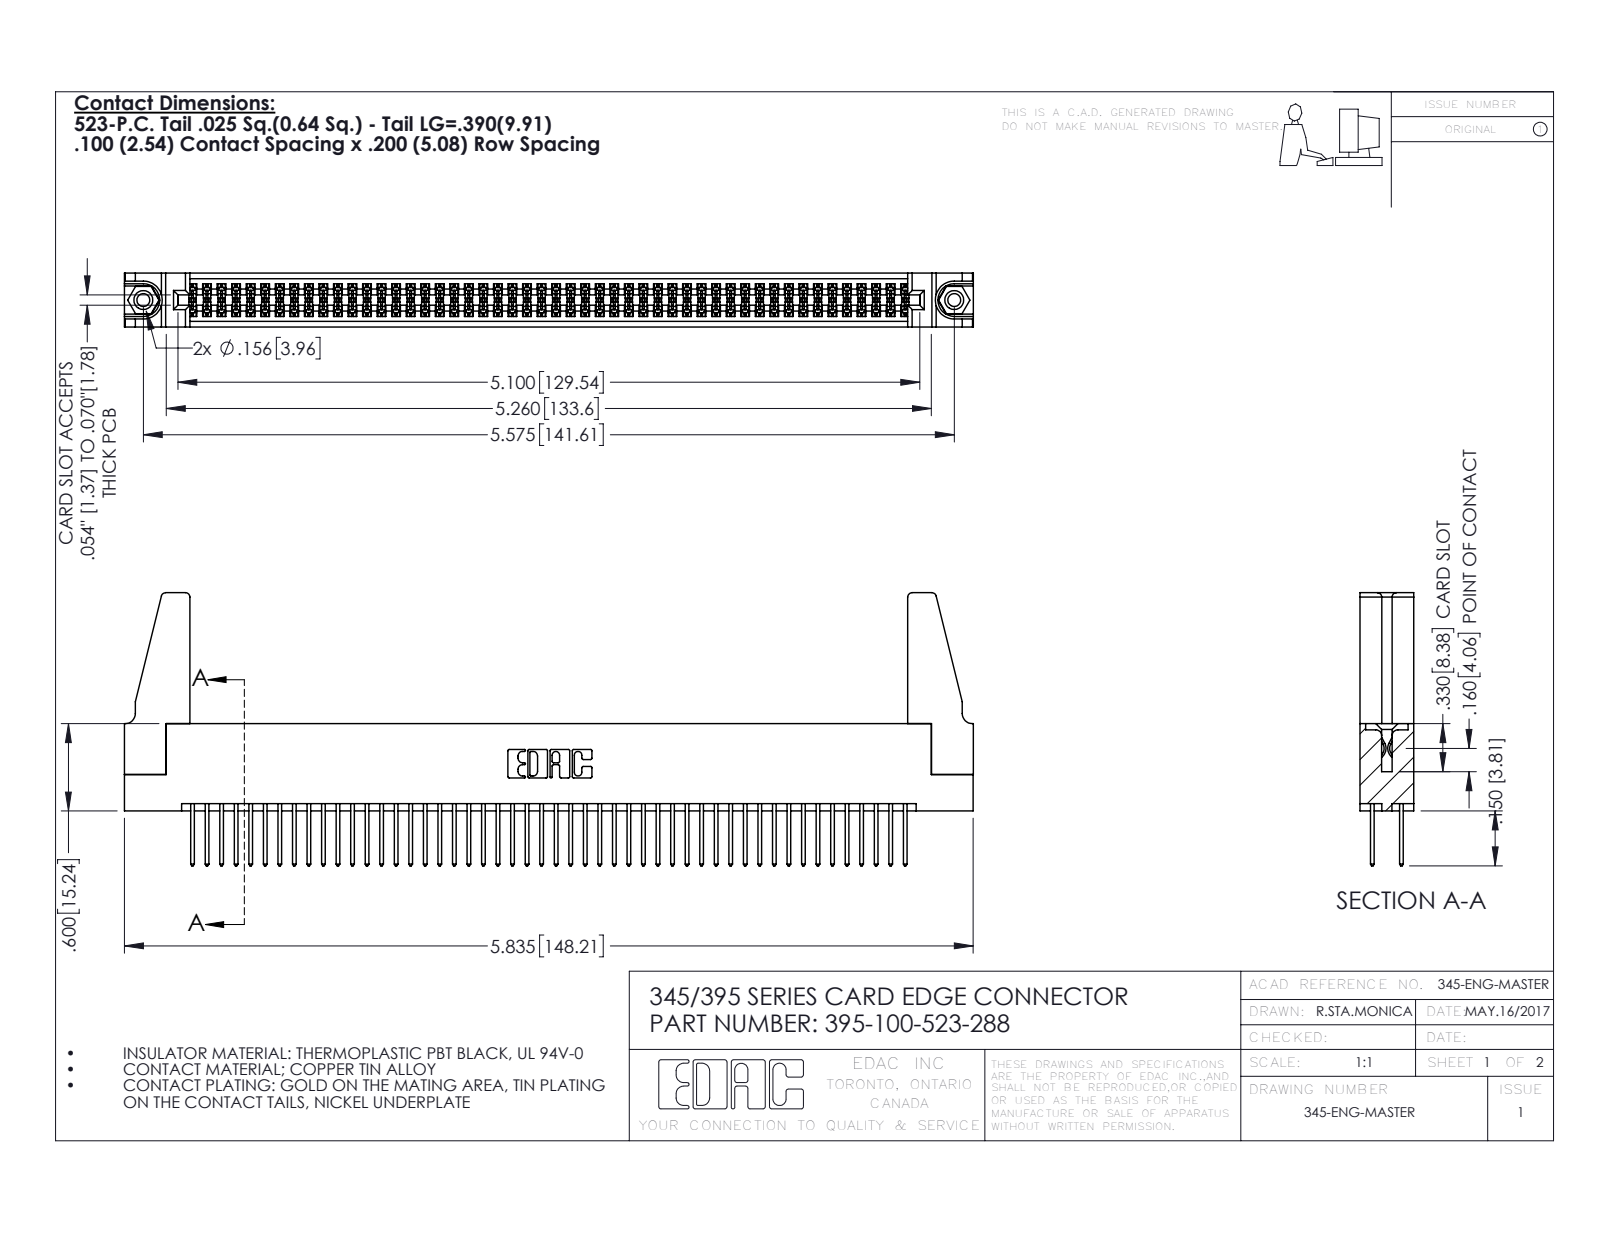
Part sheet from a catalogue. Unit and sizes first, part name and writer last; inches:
Units: inches
Overall size (bounding box): 5.836 × 1.877 × 0.37
Round holes (diameter × count): ⌀0.089 ×2, ⌀0.125 ×2, ⌀0.156 ×2, ⌀0.064 ×1
Round bosses / shafts (diameter × count): ⌀0.155 ×2
Partial cylindrical surfaces — rounded edges, fillets, slot ends (radius × count): R0.006 ×150, R0.01 ×100, R0.01 ×22, R0.03 ×8, R0.007 ×6, R0.031 ×6, R0.026 ×3, R0.014 ×2
Main face-to-face distances: 0.072, 0.298, 0.2, 0.37, 0.098, 0.272, 0.025, 0.225, 0.175, 0.149
Hole centre spacings: 0.27, 5.339, 5.575
Volume: 1.094 in³ · Surface area: 40.14 in²
Bodies: 105 solids, 5250 faces (3452 planar, 1782 cylindrical, 16 other)
Part name (STEP PRODUCT): 345-220-078_345-220-088; 345-292-001_345-293-123; 345 Part_Flush Mounting Lugs - 0.156 Dia-TH; 395-100-523-288 (+1 more)
STEP written by: SolidWorks 2016 (CONFIG_CONTROL_DESIGN)
